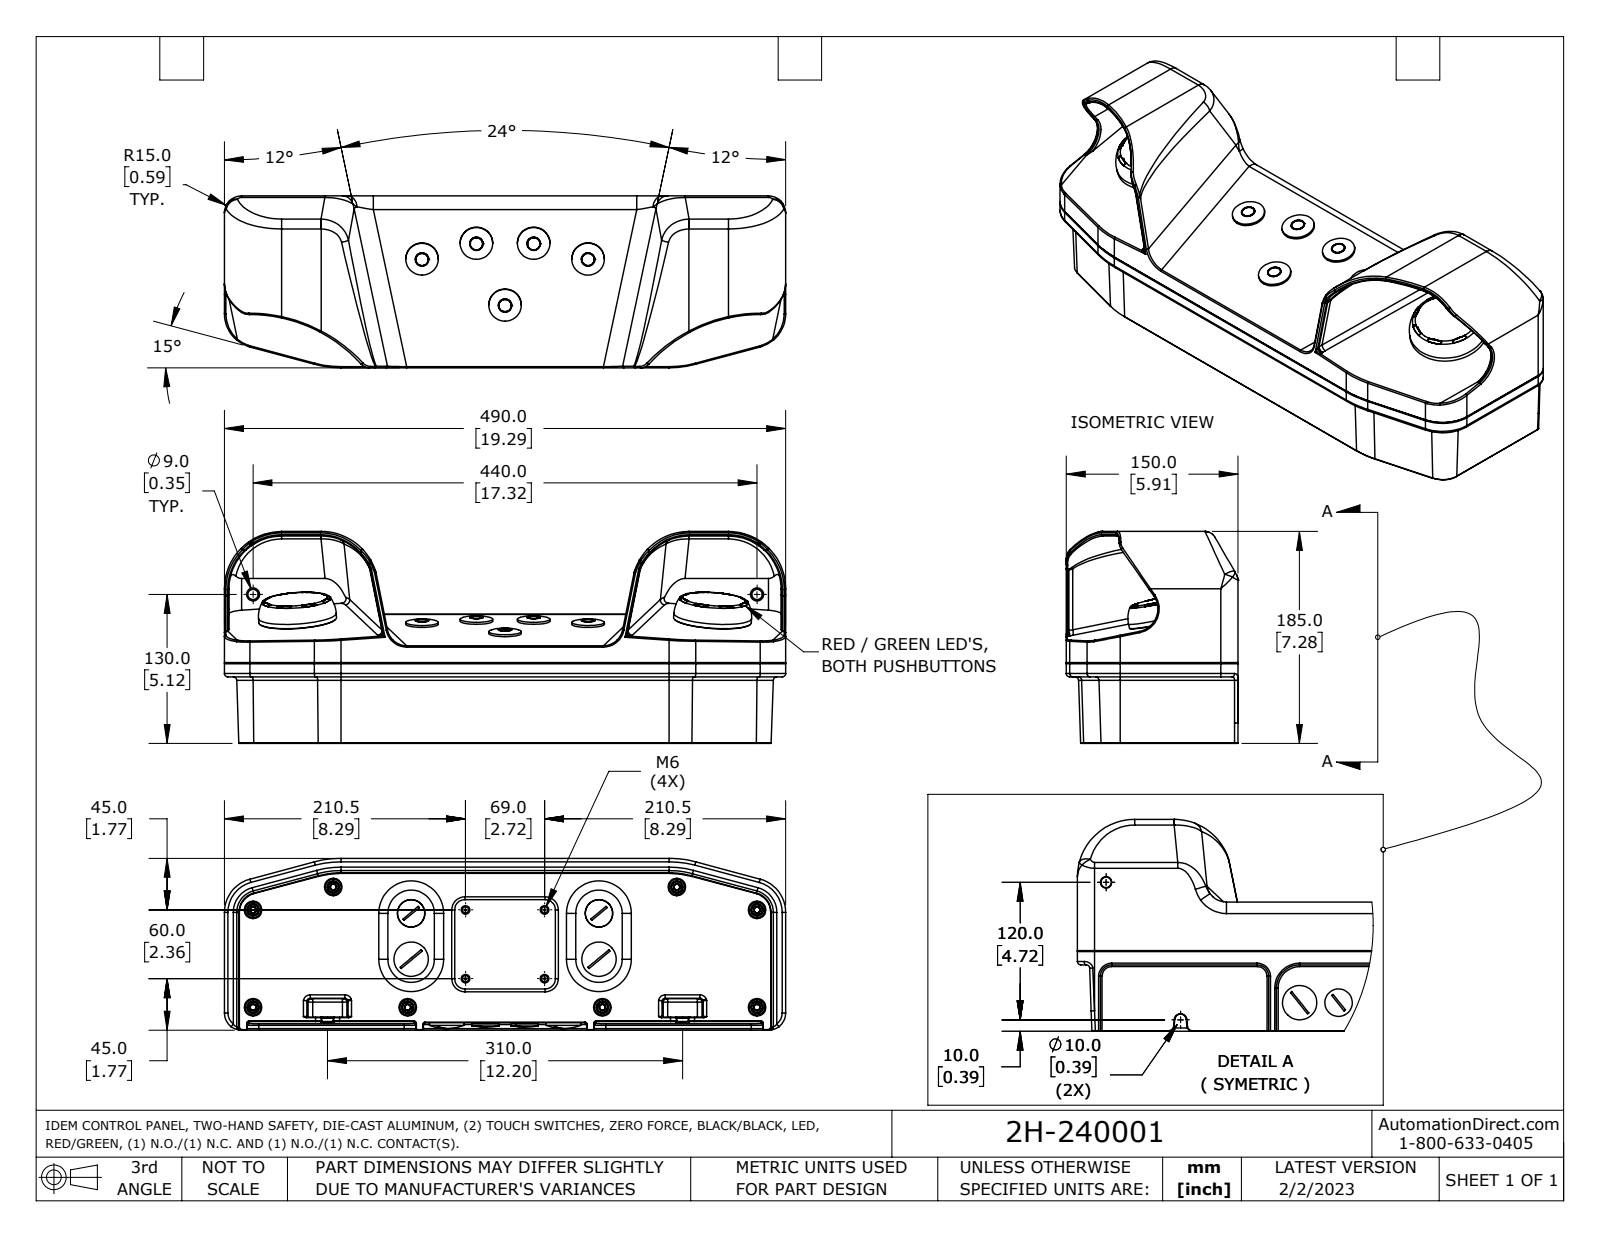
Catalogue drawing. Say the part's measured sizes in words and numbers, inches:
The part is named "2H-240001". Its 3-D file was written by "SolidWorks 2021 (AUTOMOTIVE_DESIGN)". It is 19 solids with 2538 faces: 640 planar, 1028 cylindrical and 870 other. Overall it measures 19.291 by 7.283 by 5.906 inches. Its volume is 416.1 cubic inches and its surface area 686.6 square inches. Round holes: 8 of diameter 0.528, 5 of diameter 0.433, 5 of diameter 0.626, 5 of diameter 0.886, 4 of diameter 0.083, 4 of diameter 0.197, 4 of diameter 0.217, 4 of diameter 0.571, 2 of diameter 0.354, 2 of diameter 0.701, 2 of diameter 0.78, 2 of diameter 0.969. Round bosses or shafts: 8 of diameter 0.394, 5 of diameter 1.118, 5 of diameter 0.878, 5 of diameter 0.465, 4 of diameter 1.181, 4 of diameter 0.945, 4 of diameter 0.906, 4 of diameter 0.709. Partial cylindrical surfaces (rounded edges, fillets, slot ends): 375 of radius 0.02, 116 of radius 0.012, 86 of radius 0.118, 35 of radius 0.059, 15 of radius 0.047, 10 of radius 0.394, 9 of radius 0.197, 8 of radius 0.157. The main face-to-face distances are 0.157, 0.098, 5.906, 0.256, 7.126, 5.65, 7.028, 7.283, 7.185, 0.315. The hole center spacings are 1.95, 3.878, 5.709, 2.378, 3.279, 1.043, 1.969, 3.279.
